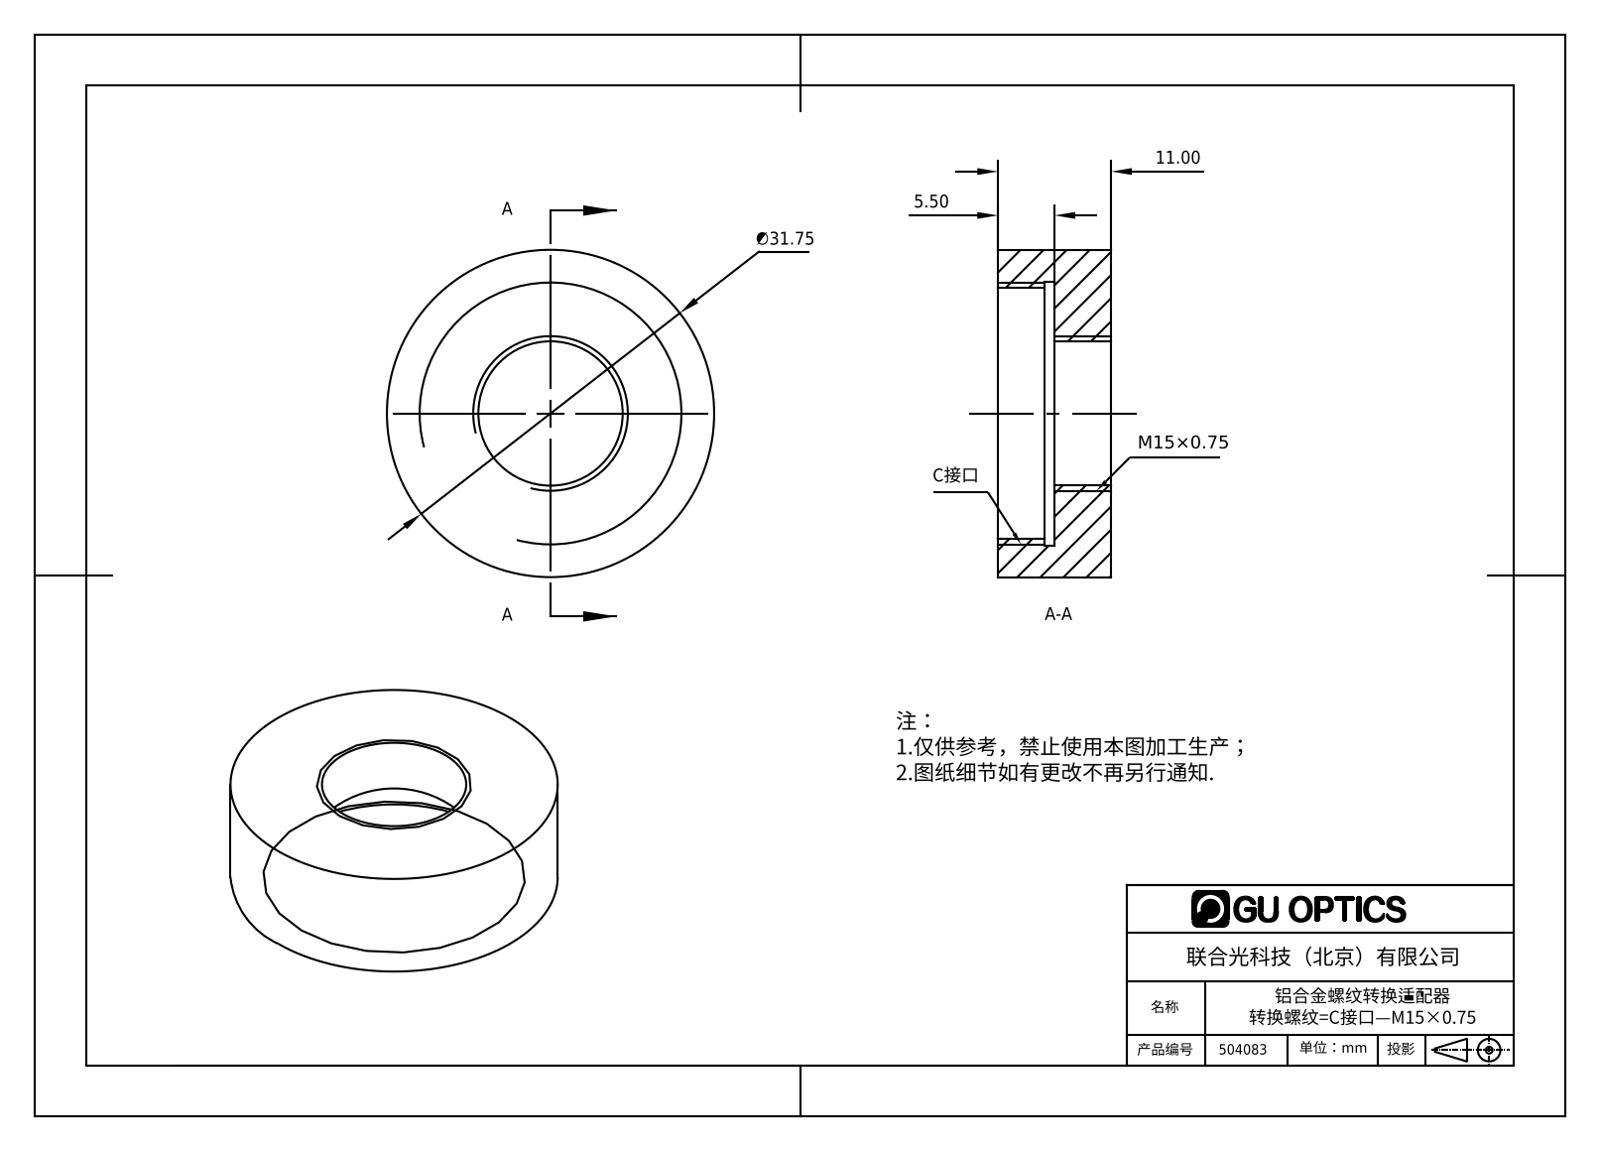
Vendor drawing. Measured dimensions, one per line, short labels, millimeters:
name: 504083
written by: SolidWorks 2016 (AUTOMOTIVE_DESIGN)
unit: mm
bodies: 1 solid, 12 faces (4 planar, 8 cylindrical, 0 other)
size: 31.75 × 31.75 × 11
volume: 5 243 mm³; area: 3 134 mm²
holes: 1× ⌀14, 1× ⌀24.4, 1× ⌀25.6
bosses: 1× ⌀31.75
face distances: 5.5, 11, 4.5, 1, 6.5
